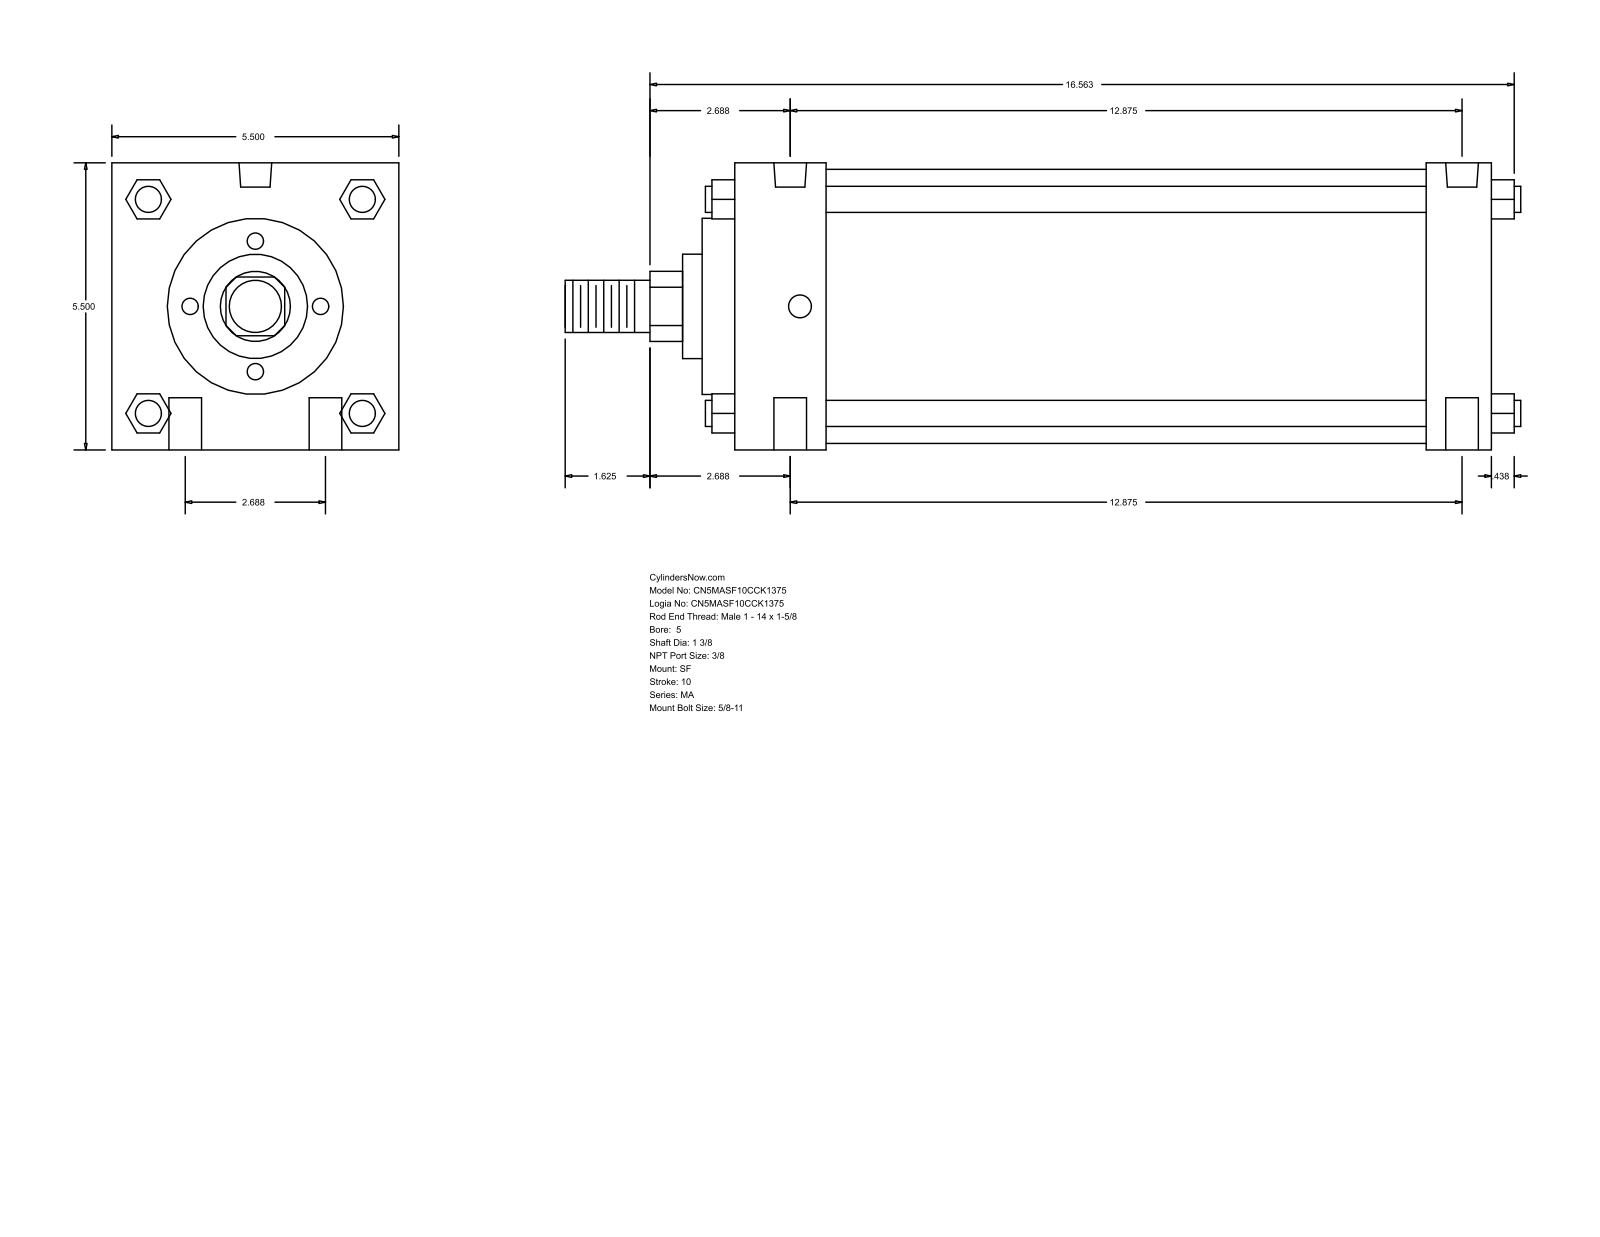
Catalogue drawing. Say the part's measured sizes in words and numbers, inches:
The part is named "MA_SF__0500_1.375". Its 3-D file was written by "GSSL Pune (CONFIG_CONTROL_DESIGN)". It is 0 solids with 126 faces: 95 planar, 31 cylindrical and 0 other. Overall it measures 18.313 by 5.5 by 5.5 inches. Round holes: 4 of diameter 0.625, 2 of diameter 0.437, 2 of diameter 0.627. Round bosses or shafts: 4 of diameter 0.5, 1 of diameter 5.25, 1 of diameter 3.375, 1 of diameter 2, 1 of diameter 1.375, 1 of diameter 1. Partial cylindrical surfaces (rounded edges, fillets, slot ends): 1 of radius 0.672. The main face-to-face distances are 5.5, 14.5, 1.75, 13.25, 11.5, 12.75, 1.25, 0.625, 2.375, 13.875. The hole center spacings are 1.344, 12.945, 12.875, 2.687, 13.153, 12.5.
